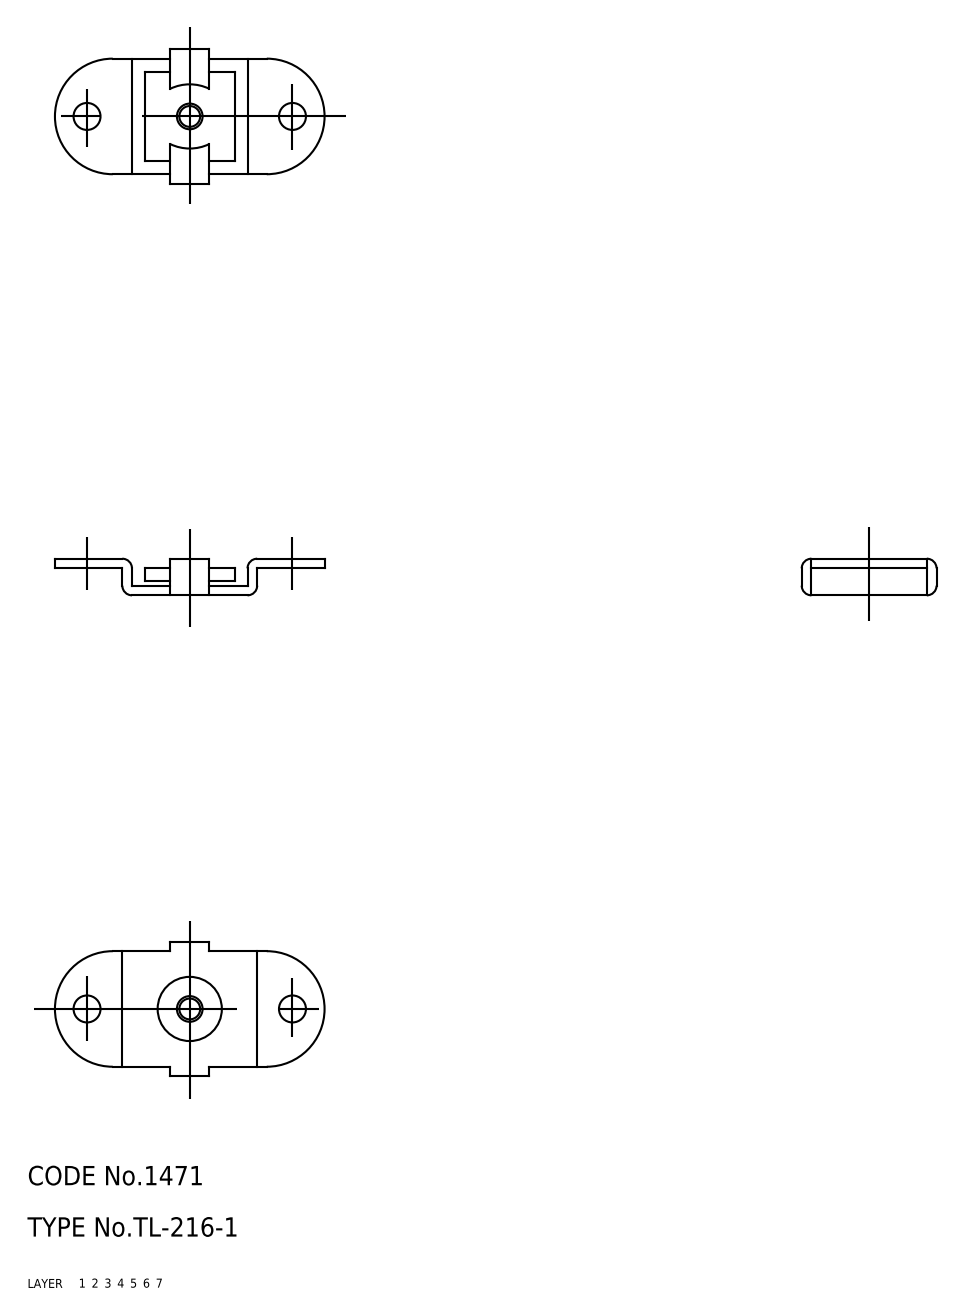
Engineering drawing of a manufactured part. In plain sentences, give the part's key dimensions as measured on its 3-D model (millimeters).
The part is named "67111377; 67111390". Its 3-D file was written by "CADfix (AUTOMOTIVE_DESIGN)". It is 2 solids with 52 faces: 0 planar, 0 cylindrical and 52 other. Overall it measures 42 by 21 by 5.7 millimeters. Its volume is 1 596 cubic millimeters and its surface area 2 467 square millimeters.
